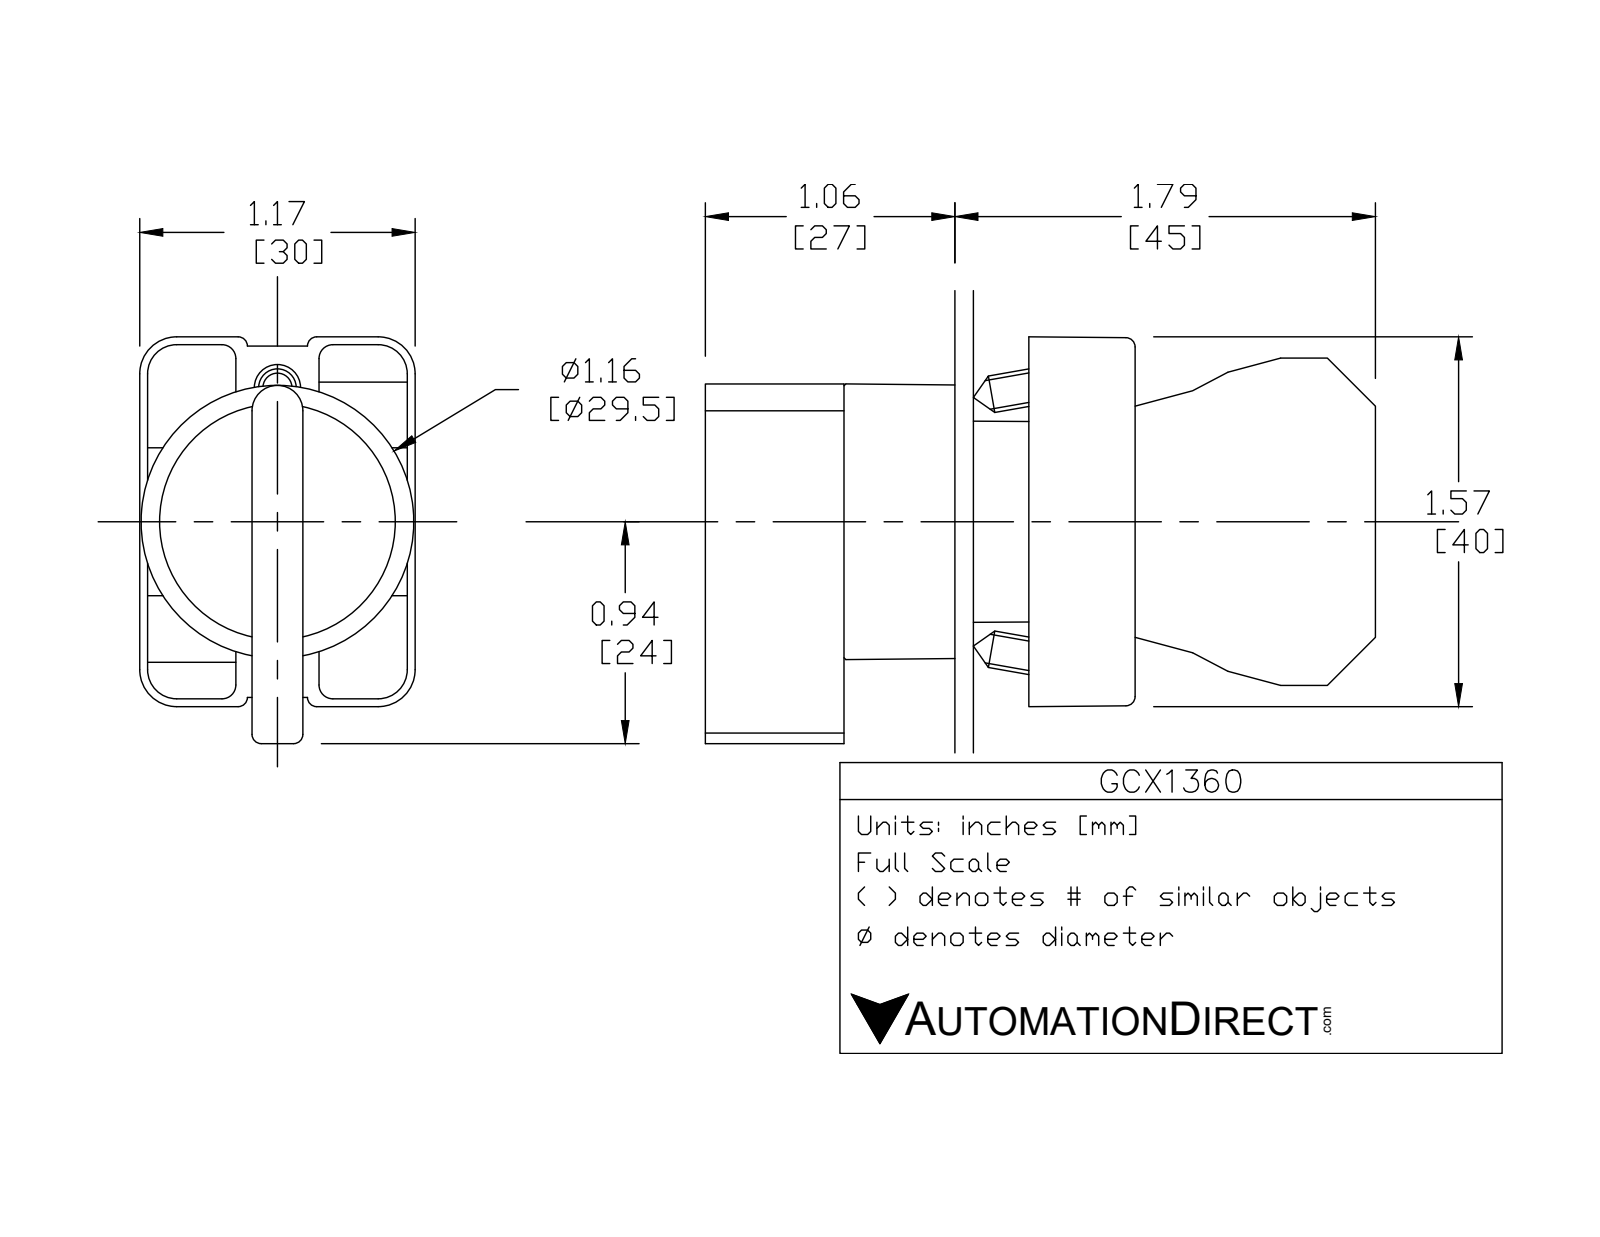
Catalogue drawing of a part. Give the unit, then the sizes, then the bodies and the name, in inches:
Units: inches
Overall size (bounding box): 2.78 × 1.752 × 1.177
Round holes (diameter × count): ⌀0.079 ×2, ⌀0.124 ×2, ⌀0.13 ×2, ⌀0.087 ×1, ⌀0.197 ×1, ⌀0.878 ×1, ⌀0.888 ×1, ⌀1.024 ×1
Round bosses / shafts (diameter × count): ⌀0.157 ×2, ⌀1.175 ×1, ⌀1.004 ×1, ⌀0.945 ×1, ⌀0.856 ×1, ⌀0.78 ×1
Partial cylindrical surfaces — rounded edges, fillets, slot ends (radius × count): R0.059 ×24, R0.041 ×12, R0.124 ×12, R0.157 ×12, R0.039 ×6, R0.128 ×2, R0.02 ×1, R0.063 ×1
Main face-to-face distances: 0.72, 0.579, 0.472, 0.033, 0.474, 0.703, 0.031, 0.124, 1.193, 1.024
Hole centre spacings: 0.236, 0.544, 0.472, 0.49
Volume: 1.929 in³ · Surface area: 29.25 in²
Bodies: 6 solids, 396 faces (232 planar, 137 cylindrical, 27 other)
Part name (STEP PRODUCT): GCX1360; ecx1040; ecx1029; GCX1360 OPERATOR
STEP written by: SolidWorks 2016 (AUTOMOTIVE_DESIGN)
